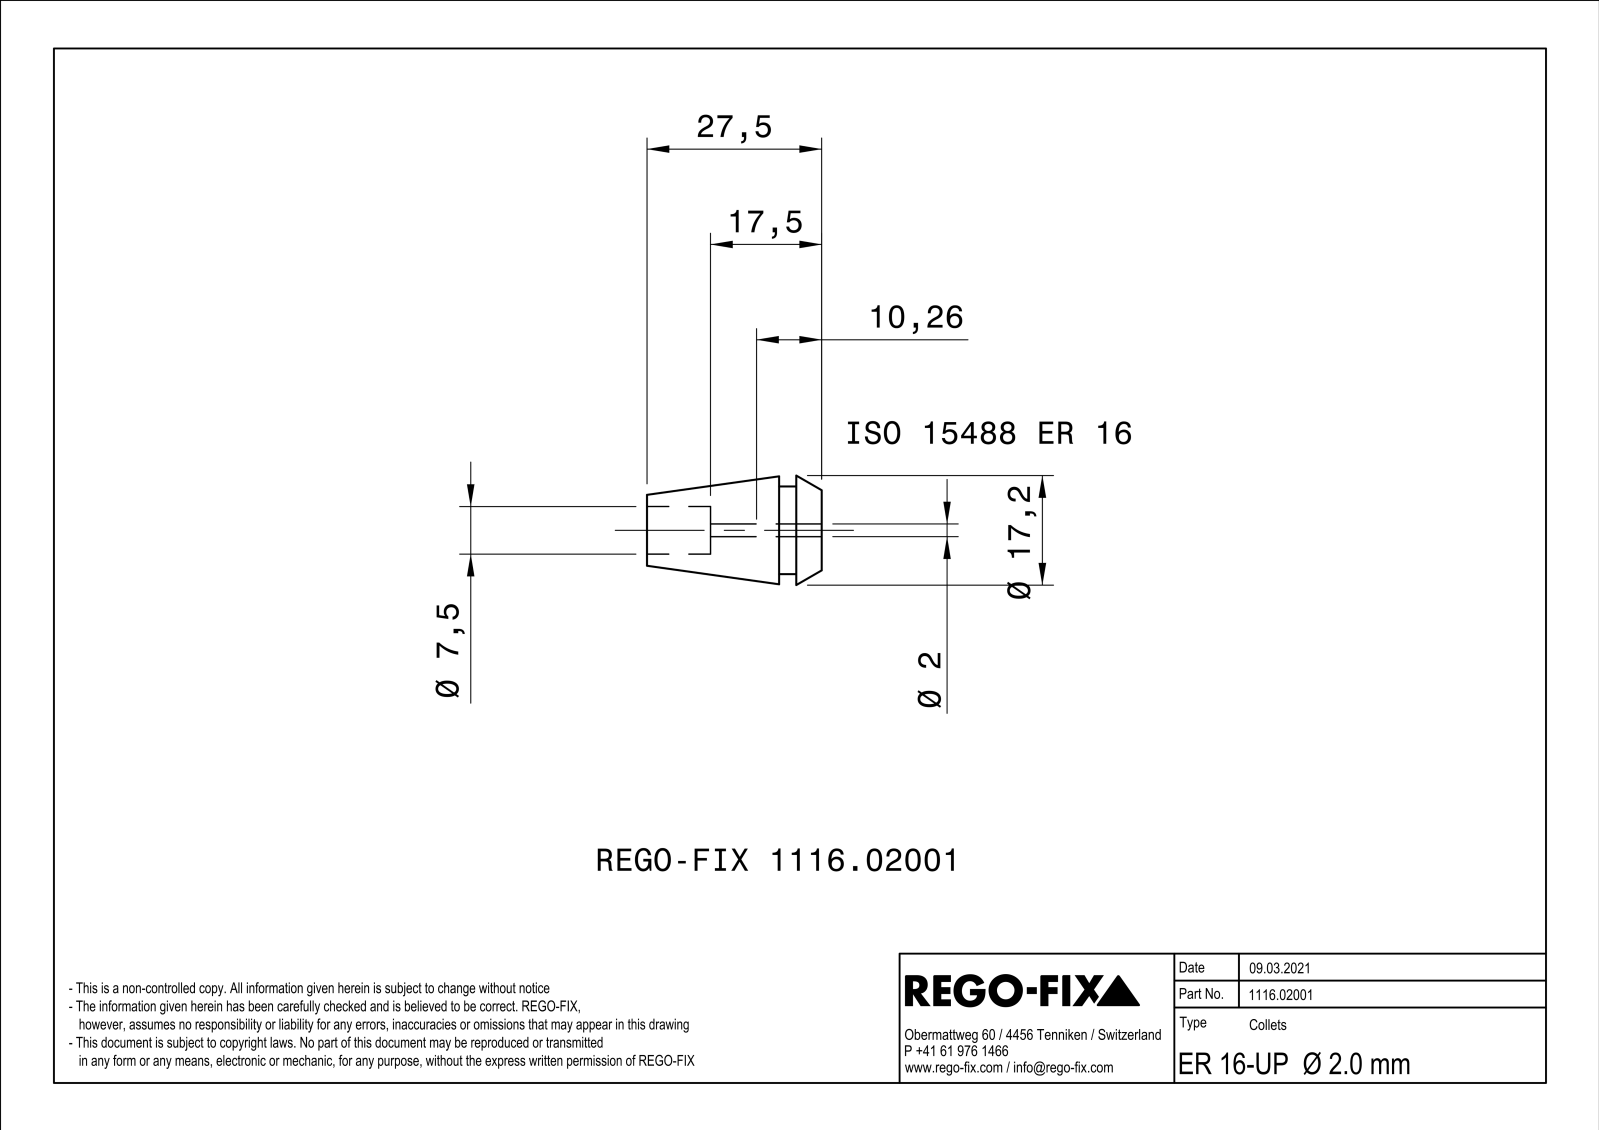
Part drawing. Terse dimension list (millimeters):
name: NOCUT
written by: SIEMENS PLM Software Solid Edge ST10 (AUTOMOTIVE_DESIGN)
unit: mm
bodies: 1 solid, 240 faces (112 planar, 32 cylindrical, 96 other)
size: 27.5 × 17.24 × 17.24
volume: 3 092 mm³; area: 5 246 mm²
holes: 1× ⌀7.5
bosses: 1× ⌀13.8
rounds: 1× R1
face distances: 0.44, 0.46, 0.45, 4, 6.7, 2.7, 3.27, 3.28, 3.72, 3.73
